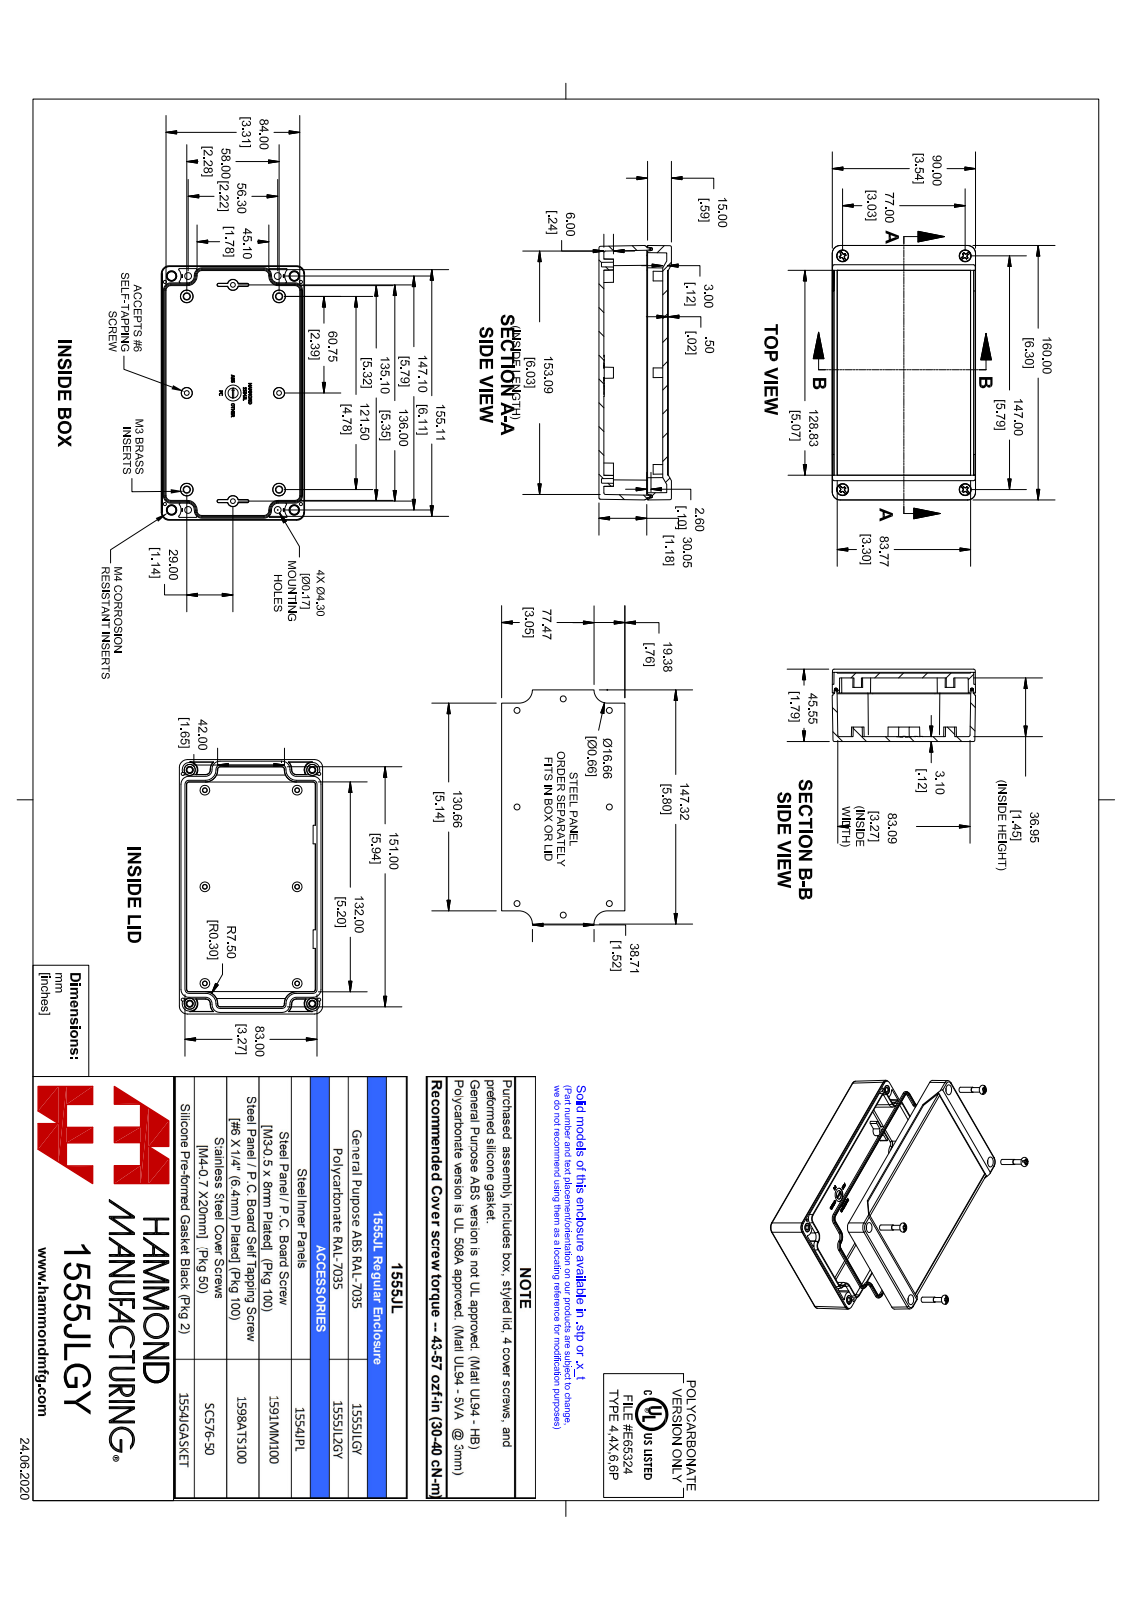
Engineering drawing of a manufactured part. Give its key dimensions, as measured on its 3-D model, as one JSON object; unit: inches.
{"part_name": "1555JLGY", "step_written_by": "SolidWorks 2021 (AUTOMOTIVE_DESIGN)", "units": "inches", "bodies": {"solids": 15, "faces": 1482, "planar": 400, "cylindrical": 323, "other": 759}, "overall_size": [6.302, 3.546, 1.793], "volume_in3": 9.898, "surface_area_in2": 182.5, "round_holes": [[0.079, 4], [0.097, 4], [0.128, 4], [0.138, 4], [0.181, 4], [0.276, 4]], "round_bosses_or_shafts": [[0.25, 4], [0.218, 4], [0.21, 4], [0.19, 4], [0.154, 4], [0.153, 4], [0.15, 4], [0.135, 4]], "partial_cylinders_radius": [[0.039, 18], [0.02, 16], [0.197, 8], [0.031, 4], [0.118, 4], [0.187, 4]], "face_to_face_distances": [0.118, 0.122, 1.695, 1.573, 1.577, 1.455, 0.12, 0.177, 0.138, 0.098], "hole_center_spacings": [0.196, 0.197, 0.626, 0.629, 0.678, 2.704, 2.707, 2.857]}
